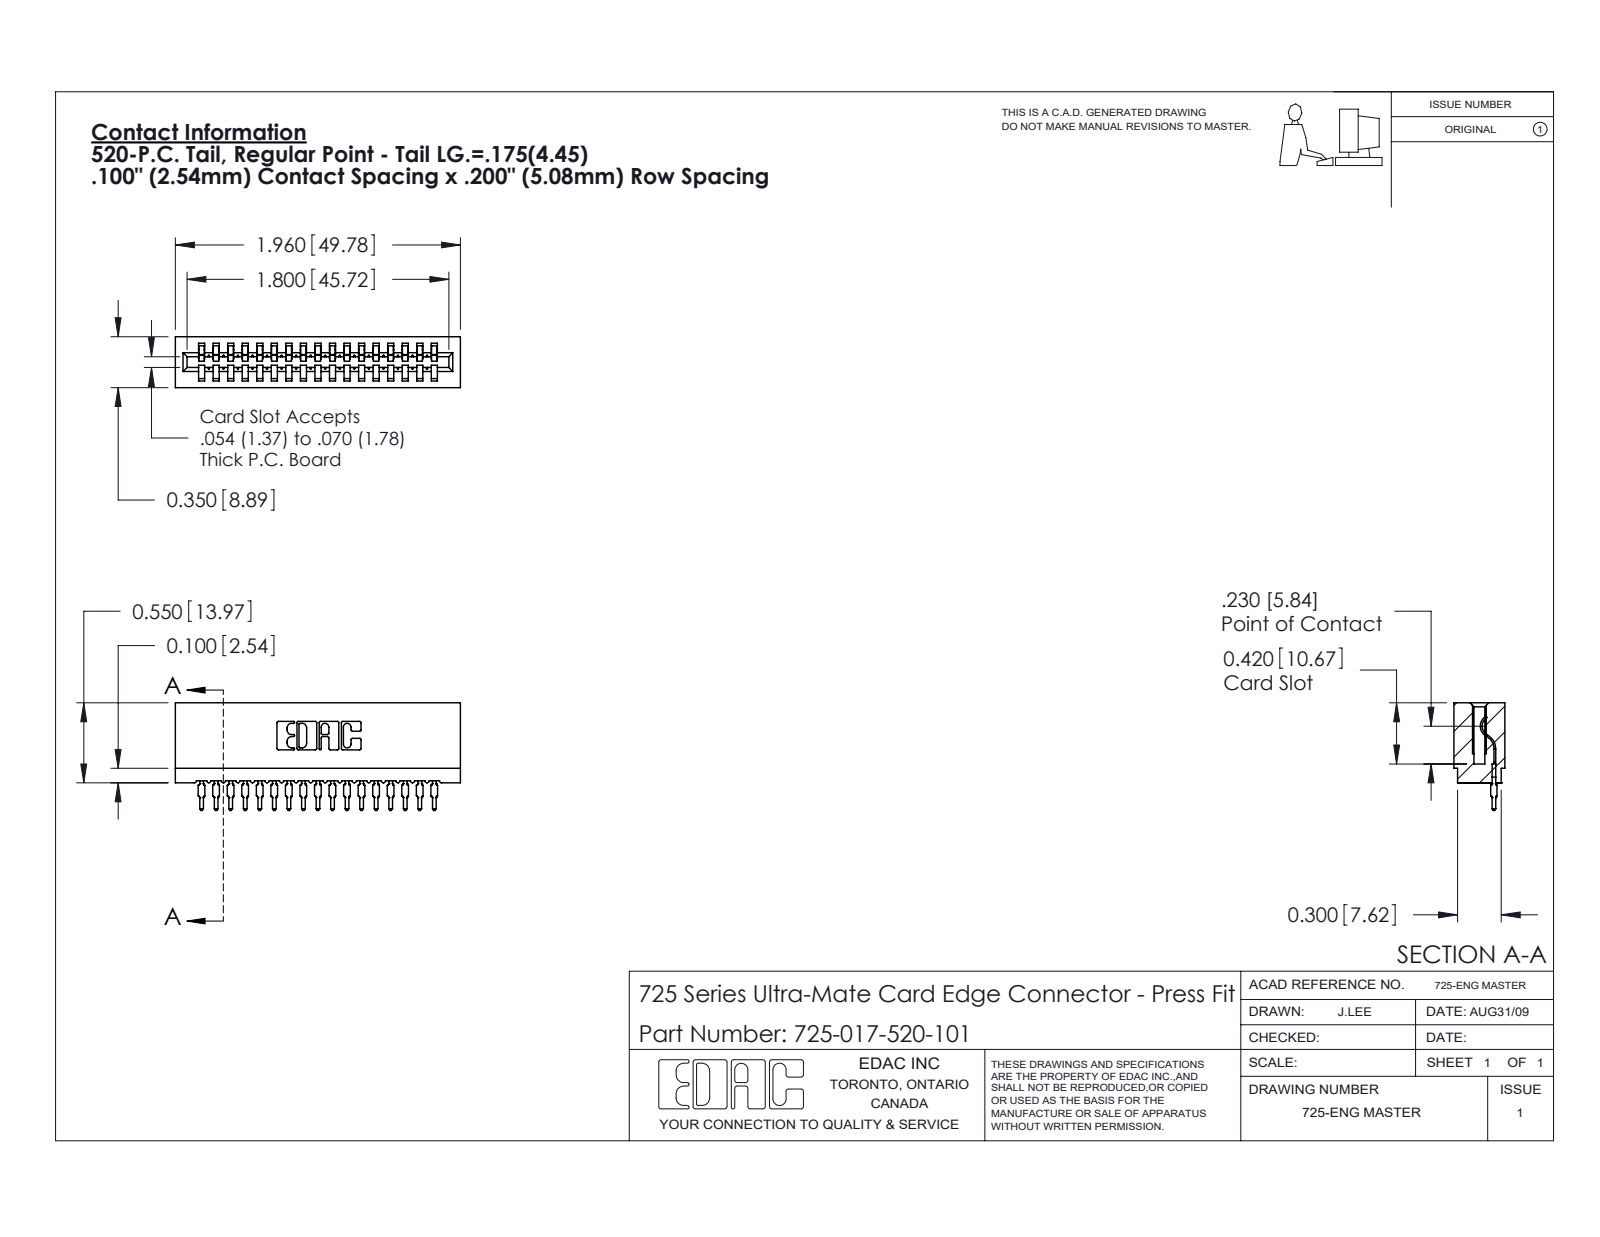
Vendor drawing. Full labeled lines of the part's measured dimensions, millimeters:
Part name (STEP PRODUCT): 725-017-520-101; 725 Part_Insulator Option - 01; 745-292-001_520
STEP written by: SolidWorks 2020 (CONFIG_CONTROL_DESIGN)
Units: millimetres
Bodies: 18 solids, 1999 faces (1194 planar, 363 cylindrical, 442 other)
Overall size (bounding box): 49.8 × 18.8 × 8.9
Volume: 3 900 mm³ · Surface area: 6 942 mm²
Partial cylindrical surfaces — rounded edges, fillets, slot ends (radius × count): R0.4 ×34, R0.5 ×34, R0.3 ×22, R0.2 ×6, R0.8 ×6, R0.1 ×4, R0.3 ×4, R0.7 ×3
Main face-to-face distances: 2.5, 5.1, 7.6, 10.2, 15.2, 12.7, 17.8, 8.9, 20.3, 5.4
